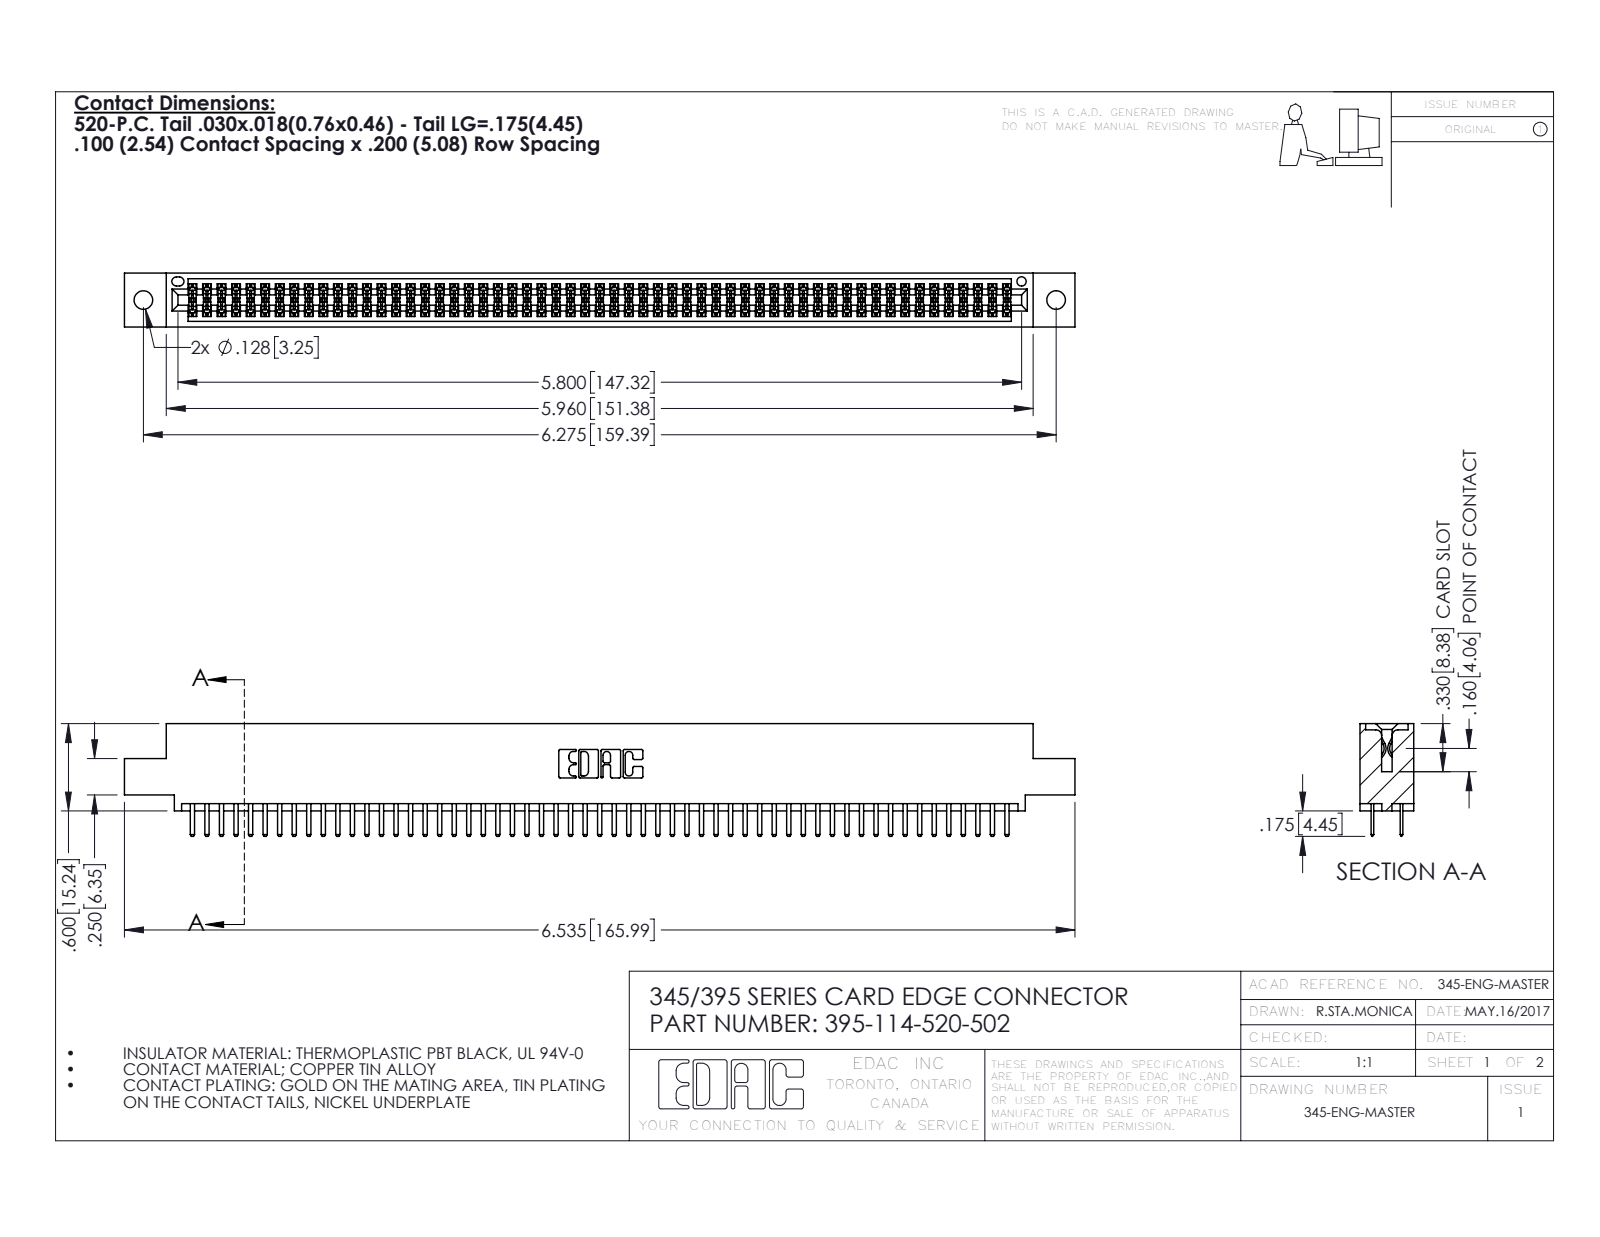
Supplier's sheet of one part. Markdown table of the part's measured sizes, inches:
| quantity | value |
| --- | --- |
| part name | 395-114-520-502; 345-292-001_345-293-120; 345 Part_0.110 Offset - 0.128 Dia |
| STEP written by | SolidWorks 2016 (CONFIG_CONTROL_DESIGN) |
| units | inches |
| bodies | 115 solids, 6286 faces (4074 planar, 2212 cylindrical, 0 other) |
| overall size | 6.535 × 0.775 × 0.37 |
| volume | 0.983 in³ |
| surface area | 36.9 in² |
| round holes (diameter × count) | 0.128 × 2, 0.064 × 1 |
| partial cylindrical surfaces (radius × count) | 0.006 × 171, 0.01 × 118, 0.01 × 22, 0.007 × 6, 0.031 × 6, 0.026 × 3, 0.014 × 2, 0.019 × 2 |
| main face-to-face distances | 0.298, 0.072, 0.2, 0.37, 0.098, 0.272, 0.025, 0.225, 0.022, 0.072 |
| hole center spacings | 0.27, 6.039, 6.275 |
